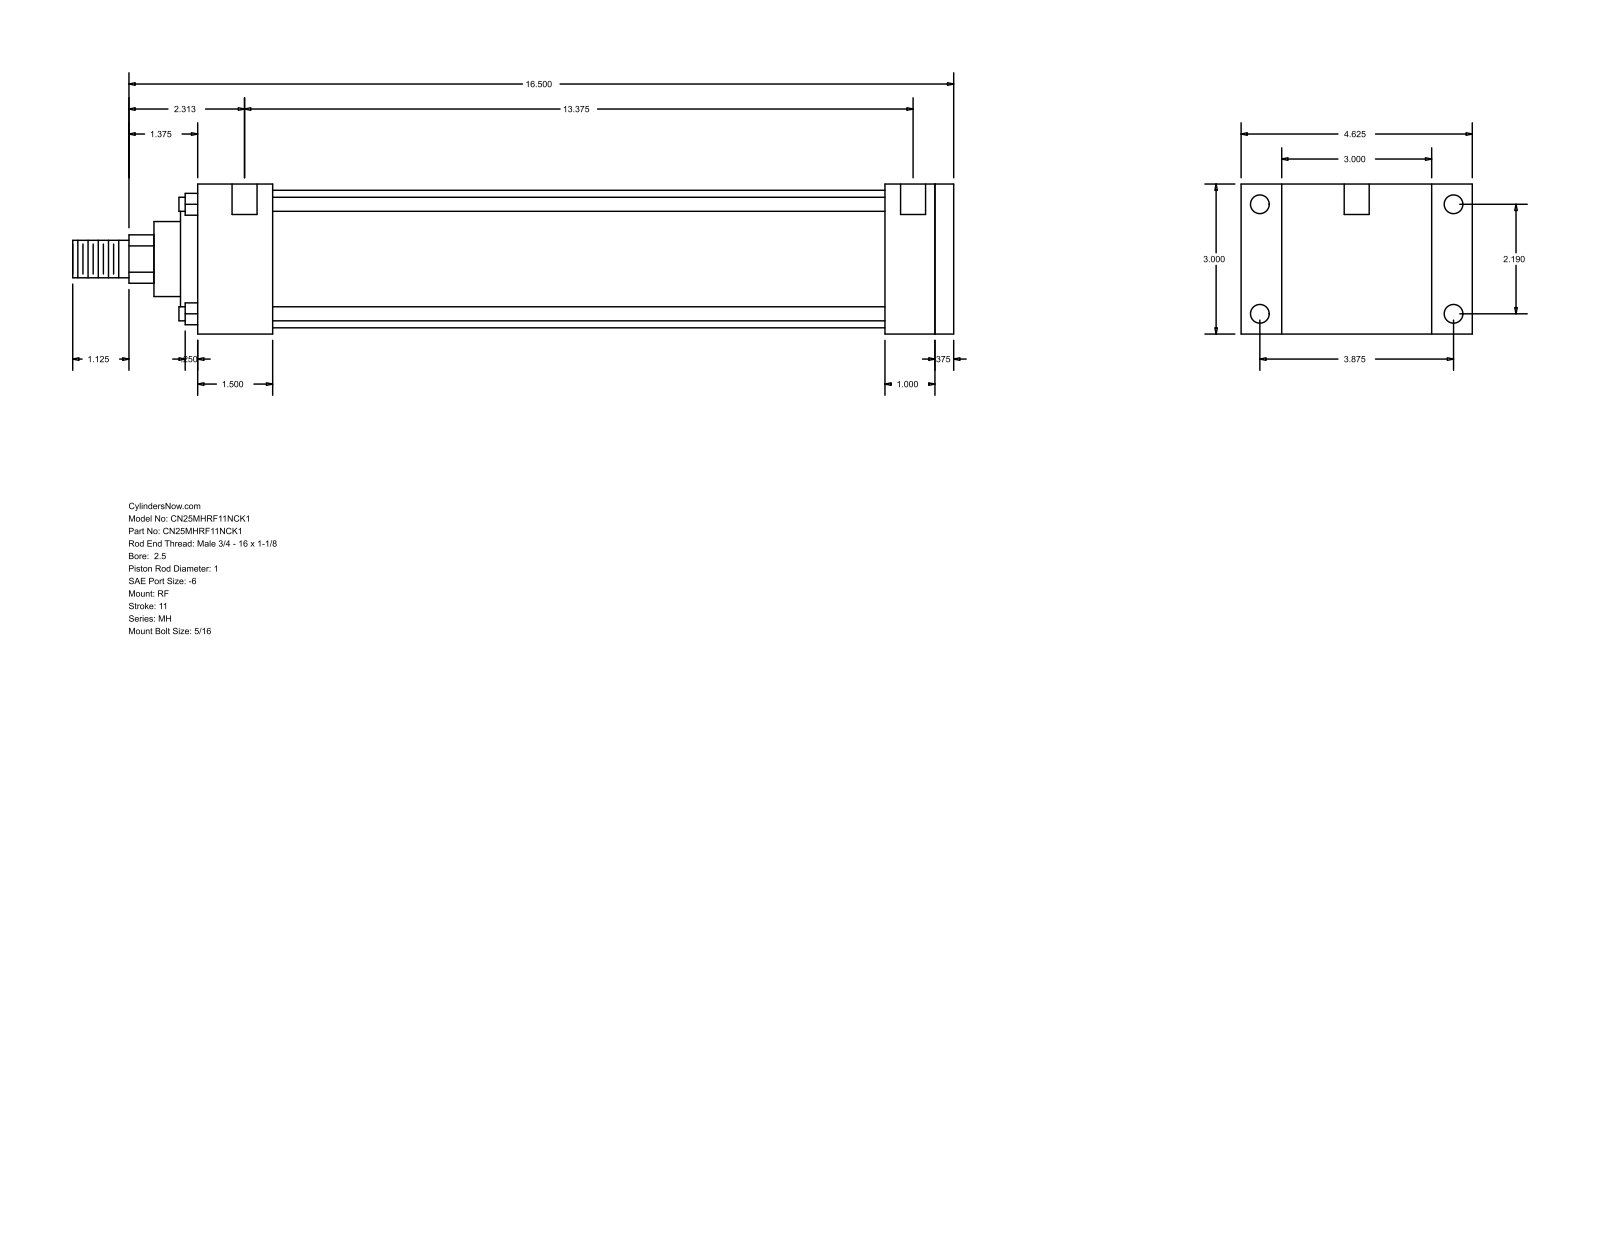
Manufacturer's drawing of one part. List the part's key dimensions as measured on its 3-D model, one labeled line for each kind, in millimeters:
Part name (STEP PRODUCT): MH_RF__0250_1
STEP written by: GSSL Pune (CONFIG_CONTROL_DESIGN)
Units: millimetres
Bodies: 0 solids, 94 faces (65 planar, 29 cylindrical, 0 other)
Overall size (bounding box): 447.68 × 117.47 × 76.2
Round holes (diameter × count): ⌀5.56 ×4, ⌀9.53 ×4, ⌀12.7 ×2
Round bosses / shafts (diameter × count): ⌀7.14 ×4, ⌀69.85 ×1, ⌀60.33 ×1, ⌀38.1 ×1, ⌀25.4 ×1, ⌀19.05 ×1
Partial cylindrical surfaces — rounded edges, fillets, slot ends (radius × count): R12.29 ×1
Main face-to-face distances: 76.2, 9.53, 384.18, 374.65, 34.92, 25.39, 349.26, 38.11, 311.15, 336.54
Hole centre spacings: 55.62, 98.42, 113.05, 347.66, 3.18, 4.76, 339.72, 342.9
